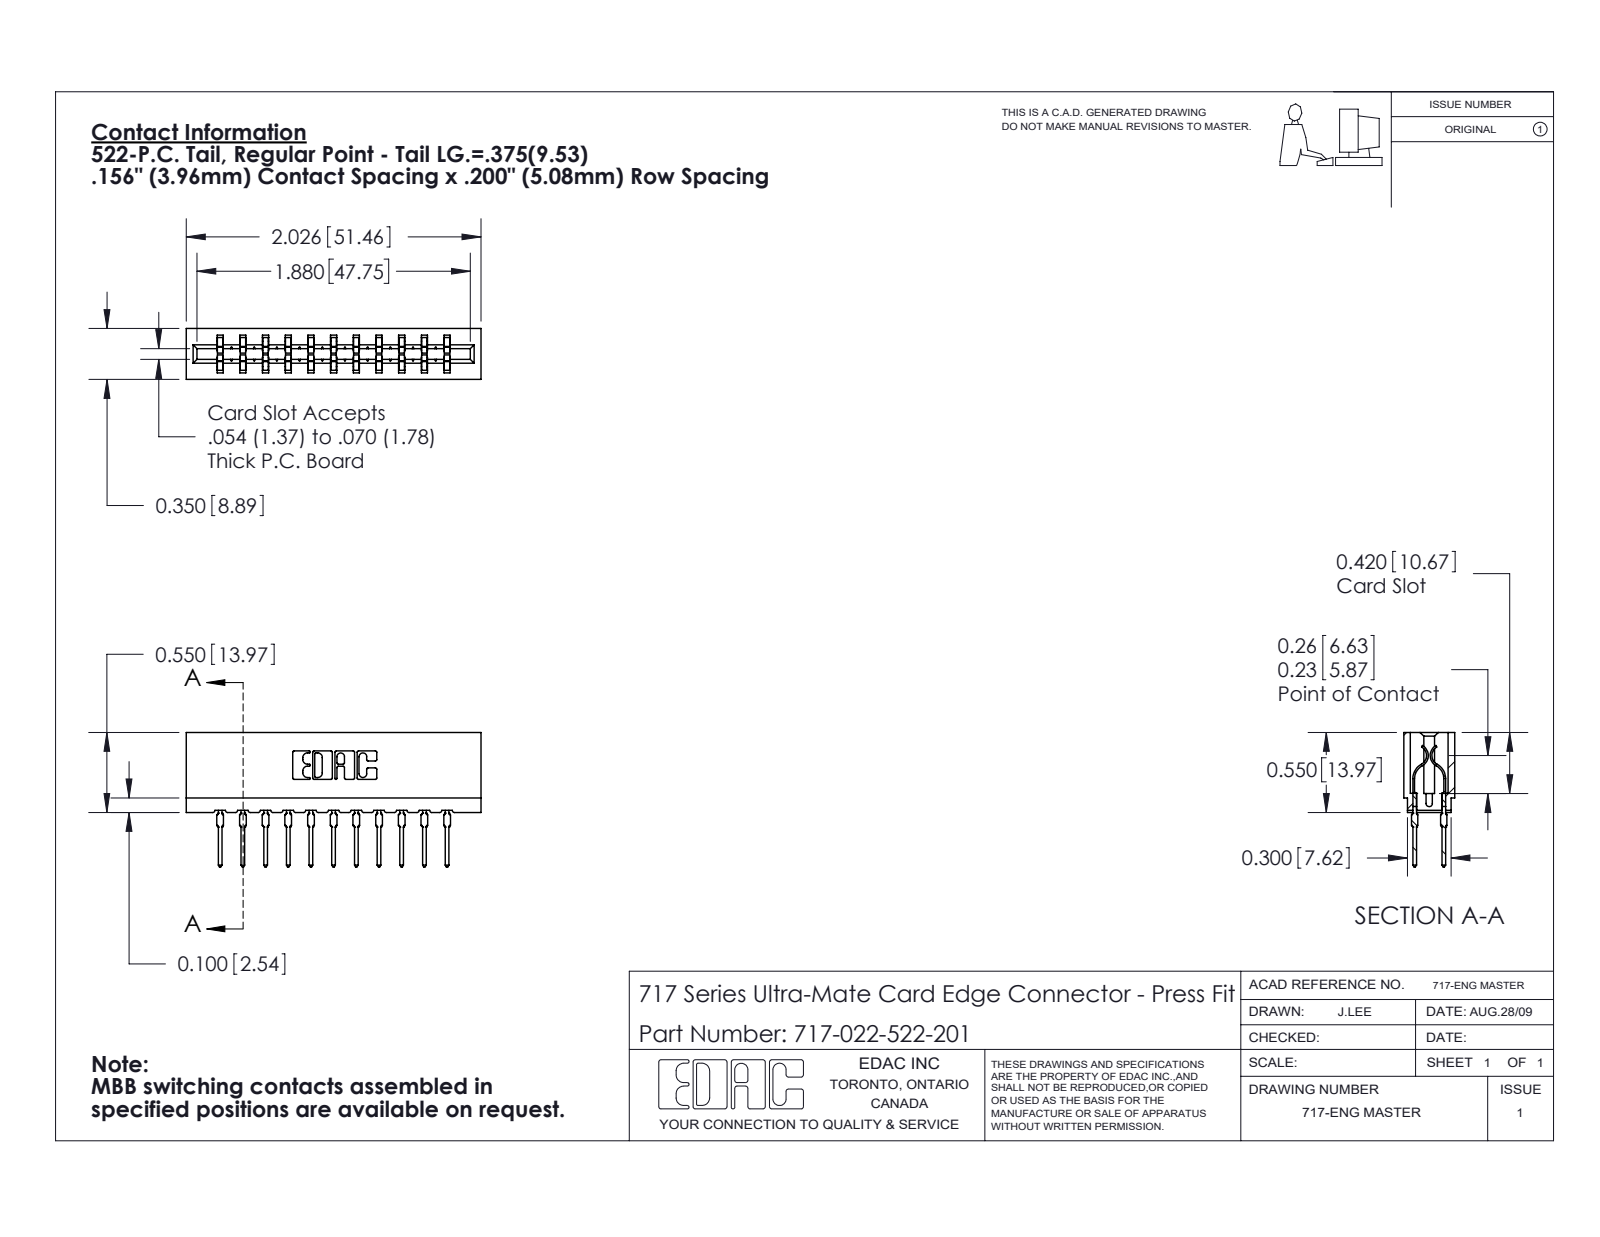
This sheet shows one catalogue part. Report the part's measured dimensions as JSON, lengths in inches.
{"part_name": "745-292-001_522; 717-022-522-201; 717 Part_Insulator Option - 06", "step_written_by": "SolidWorks 2020 (CONFIG_CONTROL_DESIGN)", "units": "inches", "bodies": {"solids": 23, "faces": 2074, "planar": 1077, "cylindrical": 425, "other": 572}, "overall_size": [2.026, 0.924, 0.35], "volume_in3": 0.281, "surface_area_in2": 10.42, "partial_cylinders_radius": [[0.021, 44], [0.01, 22], [0.015, 22], [0.005, 8], [0.011, 8], [0.007, 6], [0.031, 6], [0.026, 3]], "face_to_face_distances": [0.212, 0.156, 0.138, 0.468, 0.624, 0.35, 0.312, 0.198, 0.063, 0.287]}
